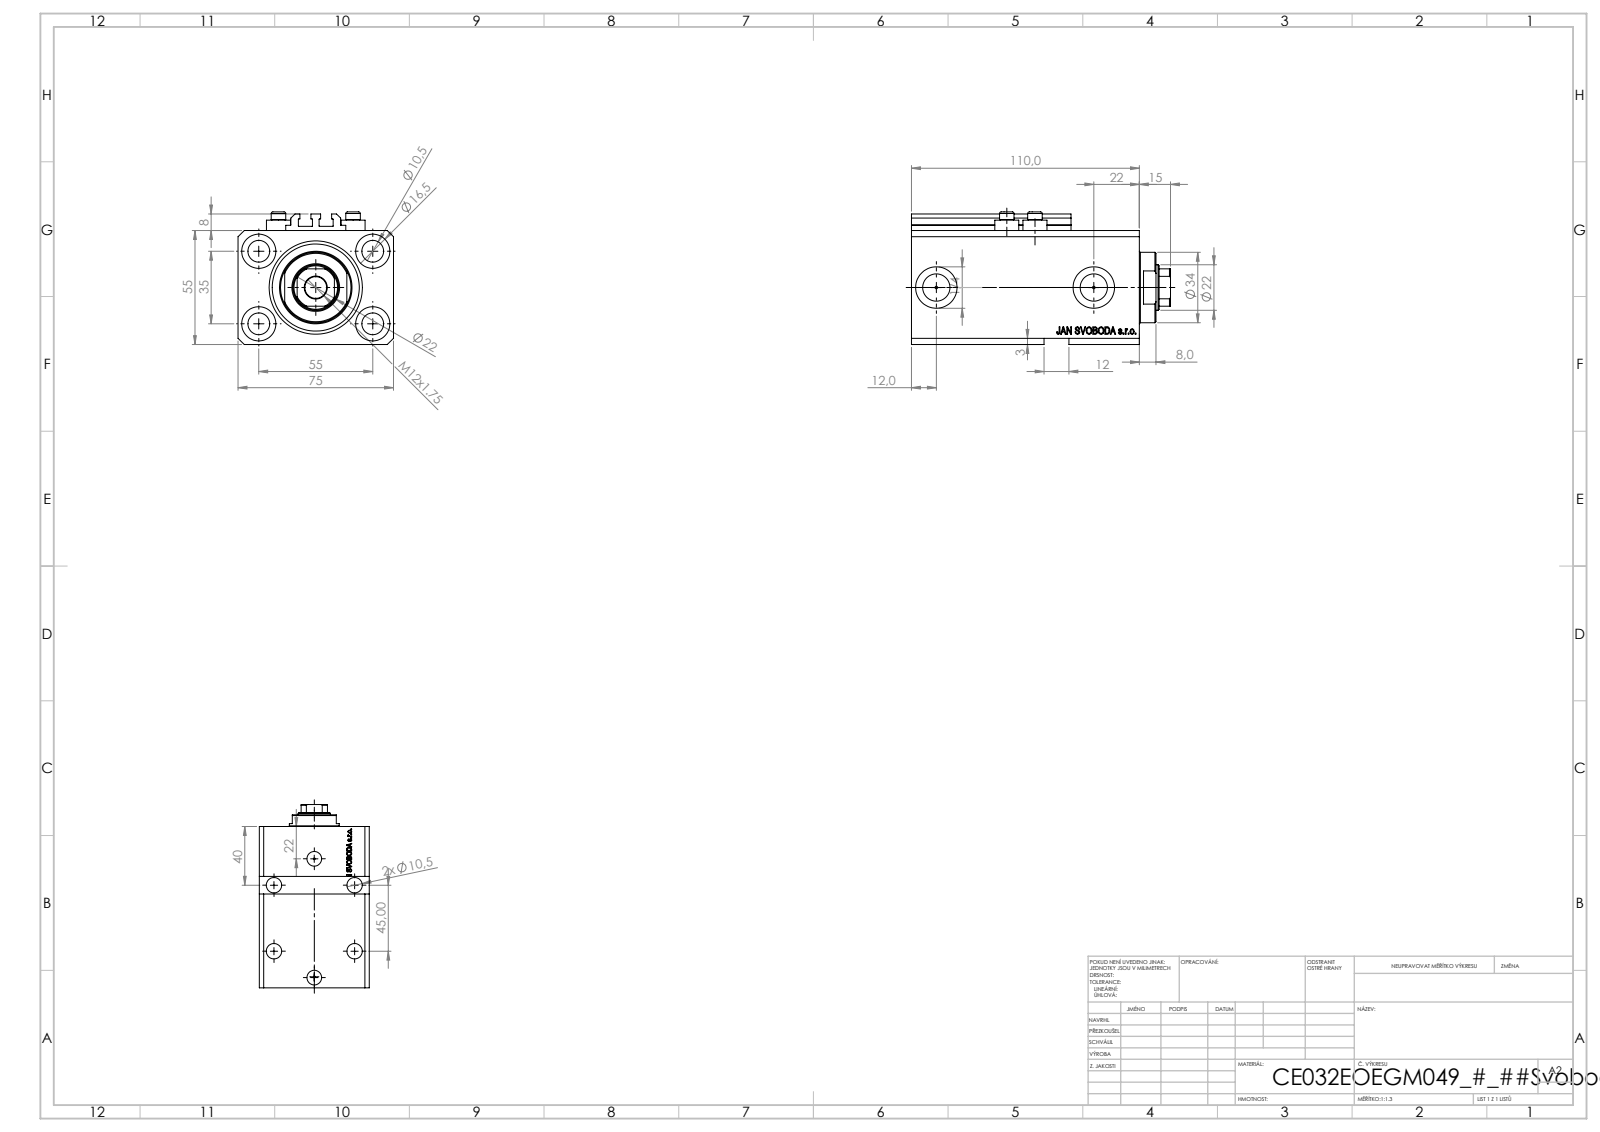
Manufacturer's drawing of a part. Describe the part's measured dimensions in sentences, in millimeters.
The part is named "V250CE_VC_E; V250CE_C_VCP; ALLEN BOLT V250CE; V250CE_E_Body". Its 3-D file was written by "SolidWorks 2019 (CONFIG_CONTROL_DESIGN)". It is 8 solids with 1084 faces: 514 planar, 146 cylindrical and 424 other. Overall it measures 125 by 75 by 64 millimeters. Its volume is 381 338 cubic millimeters and its surface area 95 642 square millimeters. Round holes: 9 of diameter 10.5, 4 of diameter 1.25, 4 of diameter 4, 4 of diameter 16.5, 2 of diameter 10, 2 of diameter 13.16, 2 of diameter 20, 1 of diameter 22, 1 of diameter 32, 1 of diameter 45. Round bosses or shafts: 4 of diameter 11.6, 4 of diameter 7, 1 of diameter 34. Partial cylindrical surfaces (rounded edges, fillets, slot ends): 10 of radius 0.2, 1 of radius 10.5. The main face-to-face distances are 55, 75, 15, 110, 95, 3, 9.9, 85.1, 100.1, 57. The hole center spacings are 32.6, 32.87, 55, 68.74, 13.6, 14.09, 23.05, 25.81.
